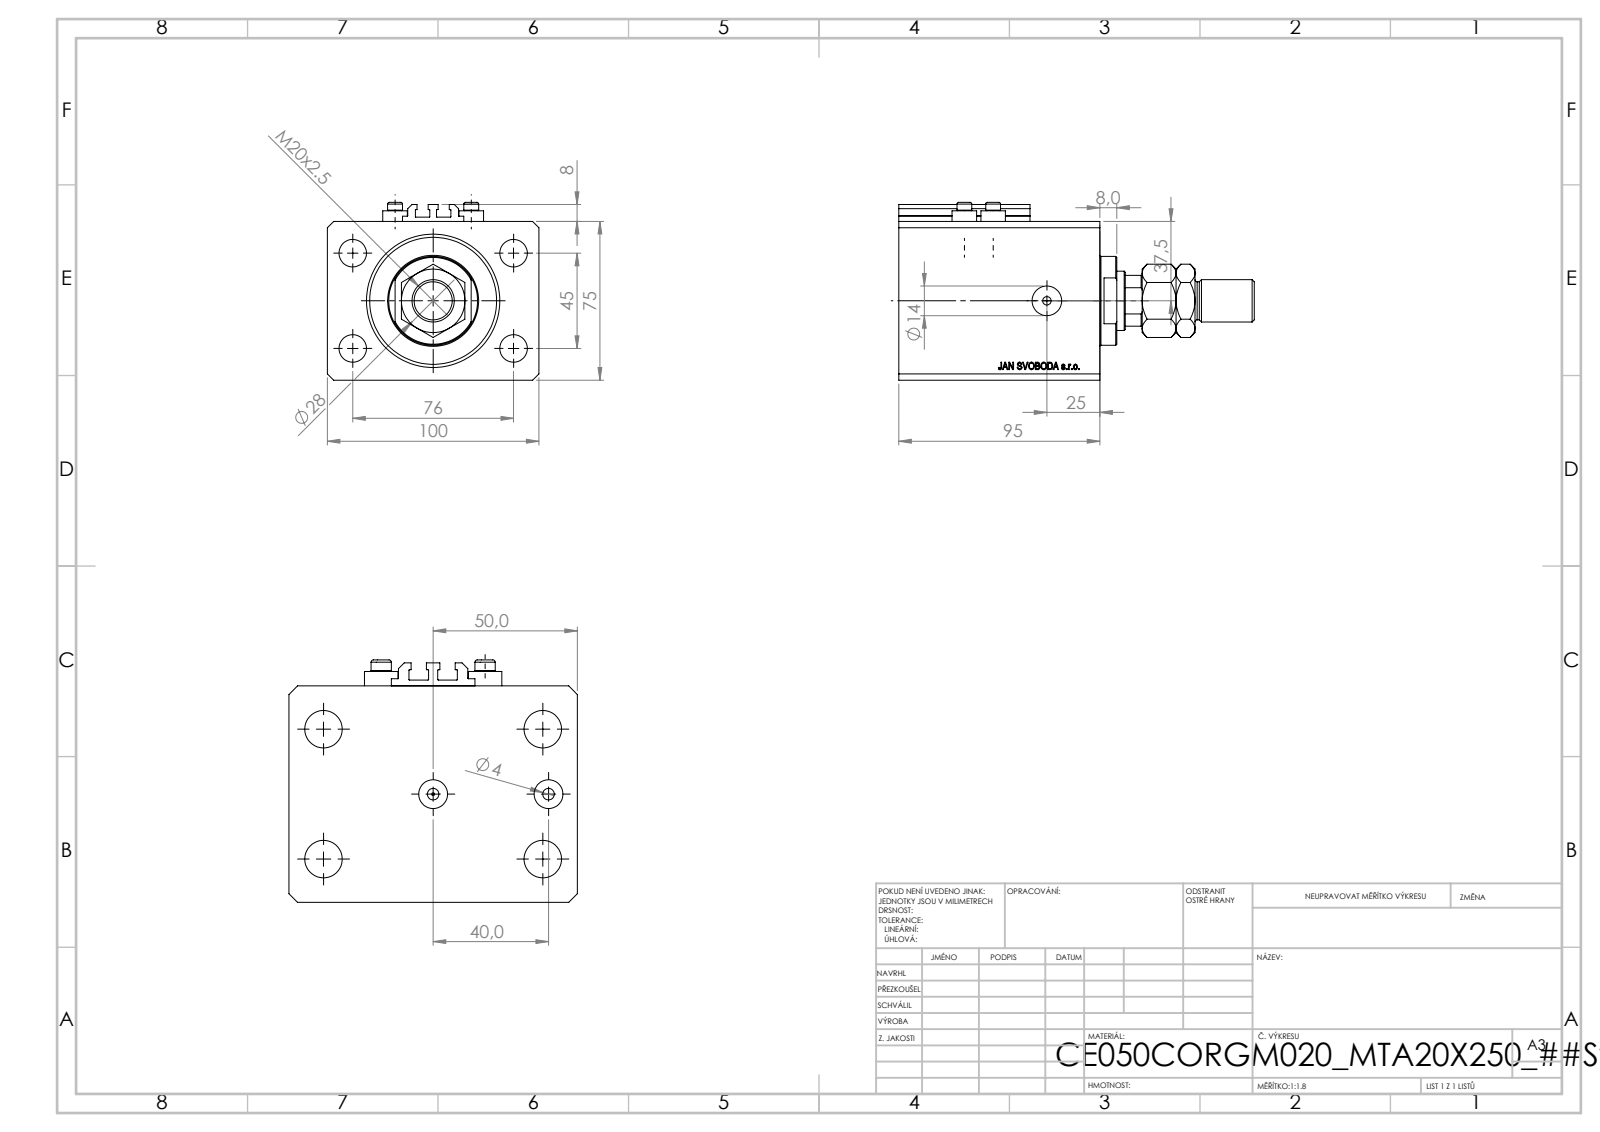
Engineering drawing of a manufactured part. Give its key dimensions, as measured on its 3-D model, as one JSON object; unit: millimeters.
{"part_name": "V250CE_VC_C; ALLEN BOLT V250CE; V250CE_C_VCP; V250CE_C_Body (+1 more)", "step_written_by": "SolidWorks 2019 (CONFIG_CONTROL_DESIGN)", "units": "millimeters", "bodies": {"solids": 9, "faces": 1087, "planar": 519, "cylindrical": 92, "other": 476}, "overall_size": [168, 100, 84], "volume_mm3": 675548, "surface_area_mm2": 123334, "round_holes": [[4, 8], [13, 4], [10, 2], [14, 2], [1.25, 1], [18.5, 1], [28, 1], [50, 1], [63, 1]], "round_bosses_or_shafts": [[11.6, 4], [7, 4], [42, 1], [20, 1], [18, 1]], "partial_cylinders_radius": [[0.2, 10], [13.5, 1]], "face_to_face_distances": [75, 100, 20, 95, 11.9, 83.1, 63.1, 40, 3, 65], "hole_center_spacings": [44.16, 45, 13.6, 22.59, 36, 38.48, 76, 81.18]}
